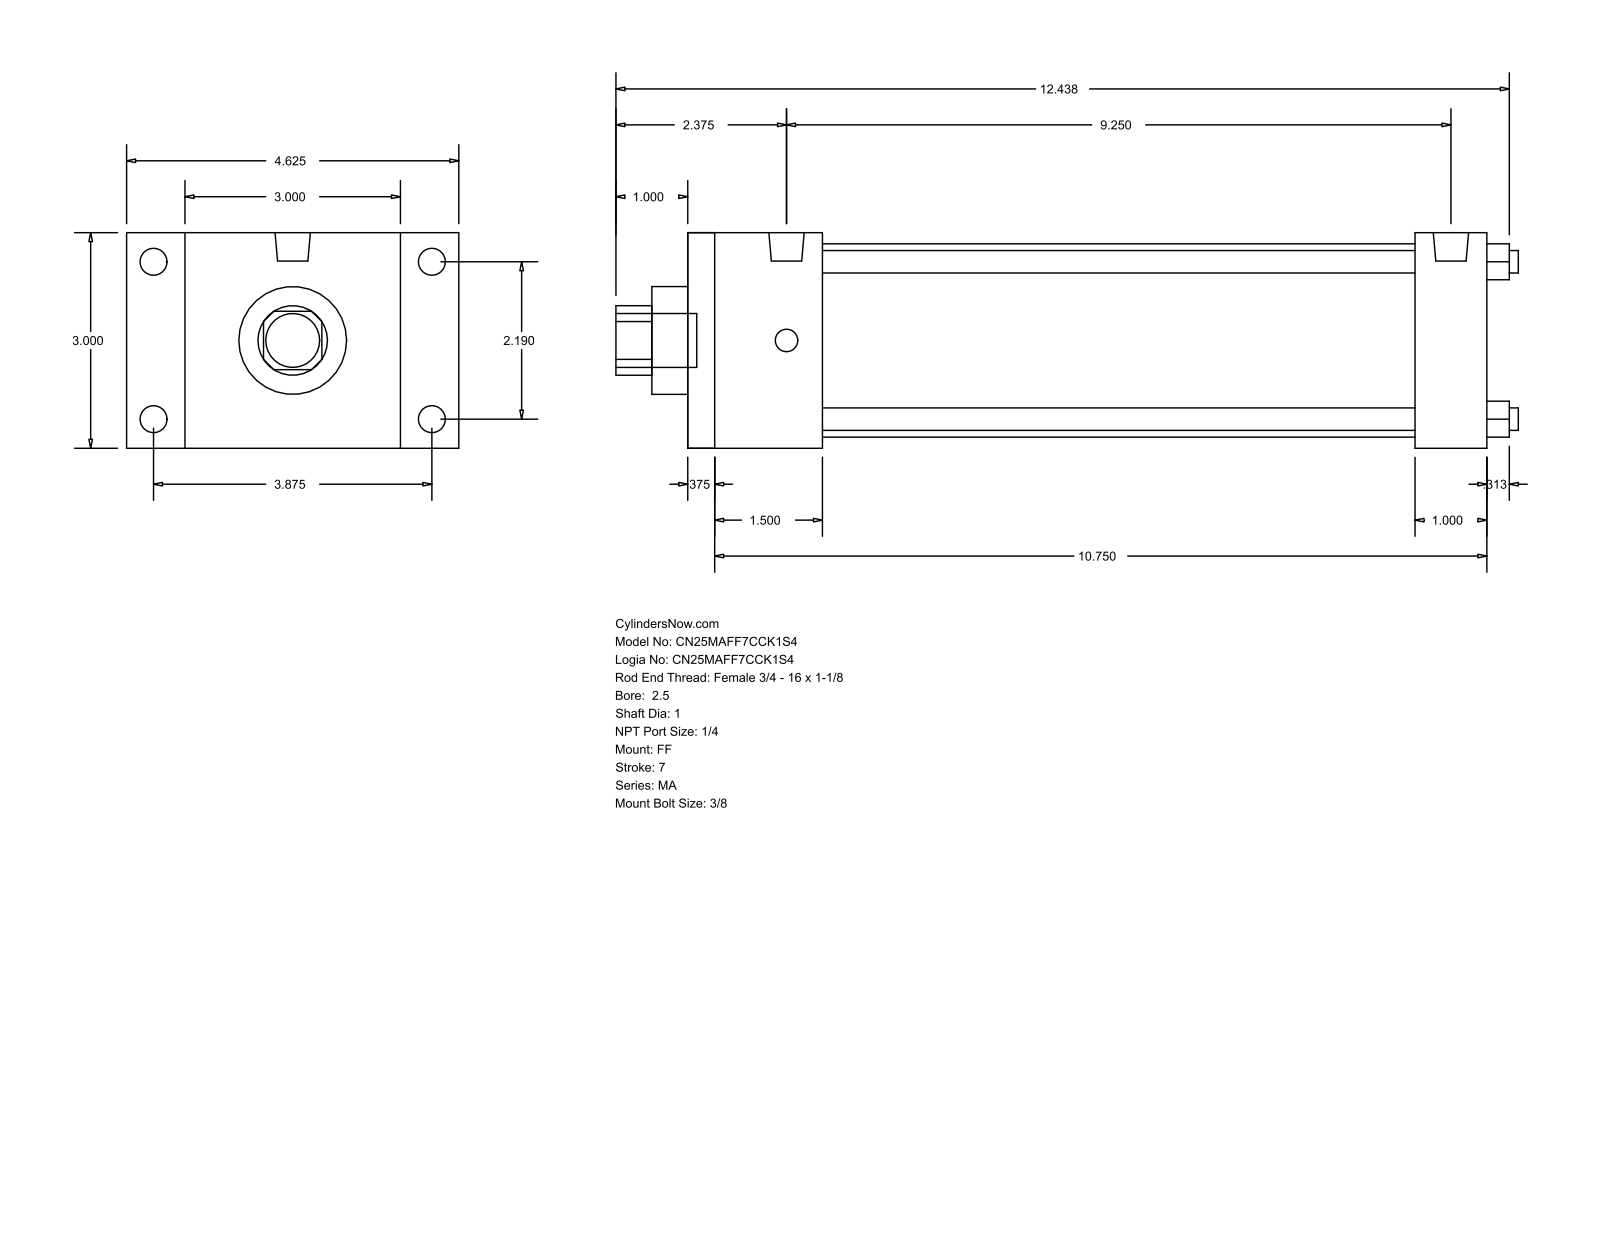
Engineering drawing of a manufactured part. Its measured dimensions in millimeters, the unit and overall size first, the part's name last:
Units: millimetres
Overall size (bounding box): 319.09 × 117.47 × 76.2
Round holes (diameter × count): ⌀7.94 ×4, ⌀25.4 ×1, ⌀38.1 ×1, ⌀68.33 ×1
Round bosses / shafts (diameter × count): ⌀9.53 ×4, ⌀7.94 ×4, ⌀12.49 ×2, ⌀19.05 ×1
Partial cylindrical surfaces — rounded edges, fillets, slot ends (radius × count): R12.29 ×1
Main face-to-face distances: 76.2, 282.58, 9.52, 273.06, 47.63, 257.17, 38.11, 247.65, 209.54, 234.95
Hole centre spacings: 39.33, 55.62, 78.66
Bodies: 0 solids, 92 faces (64 planar, 28 cylindrical, 0 other)
Part name (STEP PRODUCT): MA_FF__0250_1
STEP written by: GSSL Pune (CONFIG_CONTROL_DESIGN)
